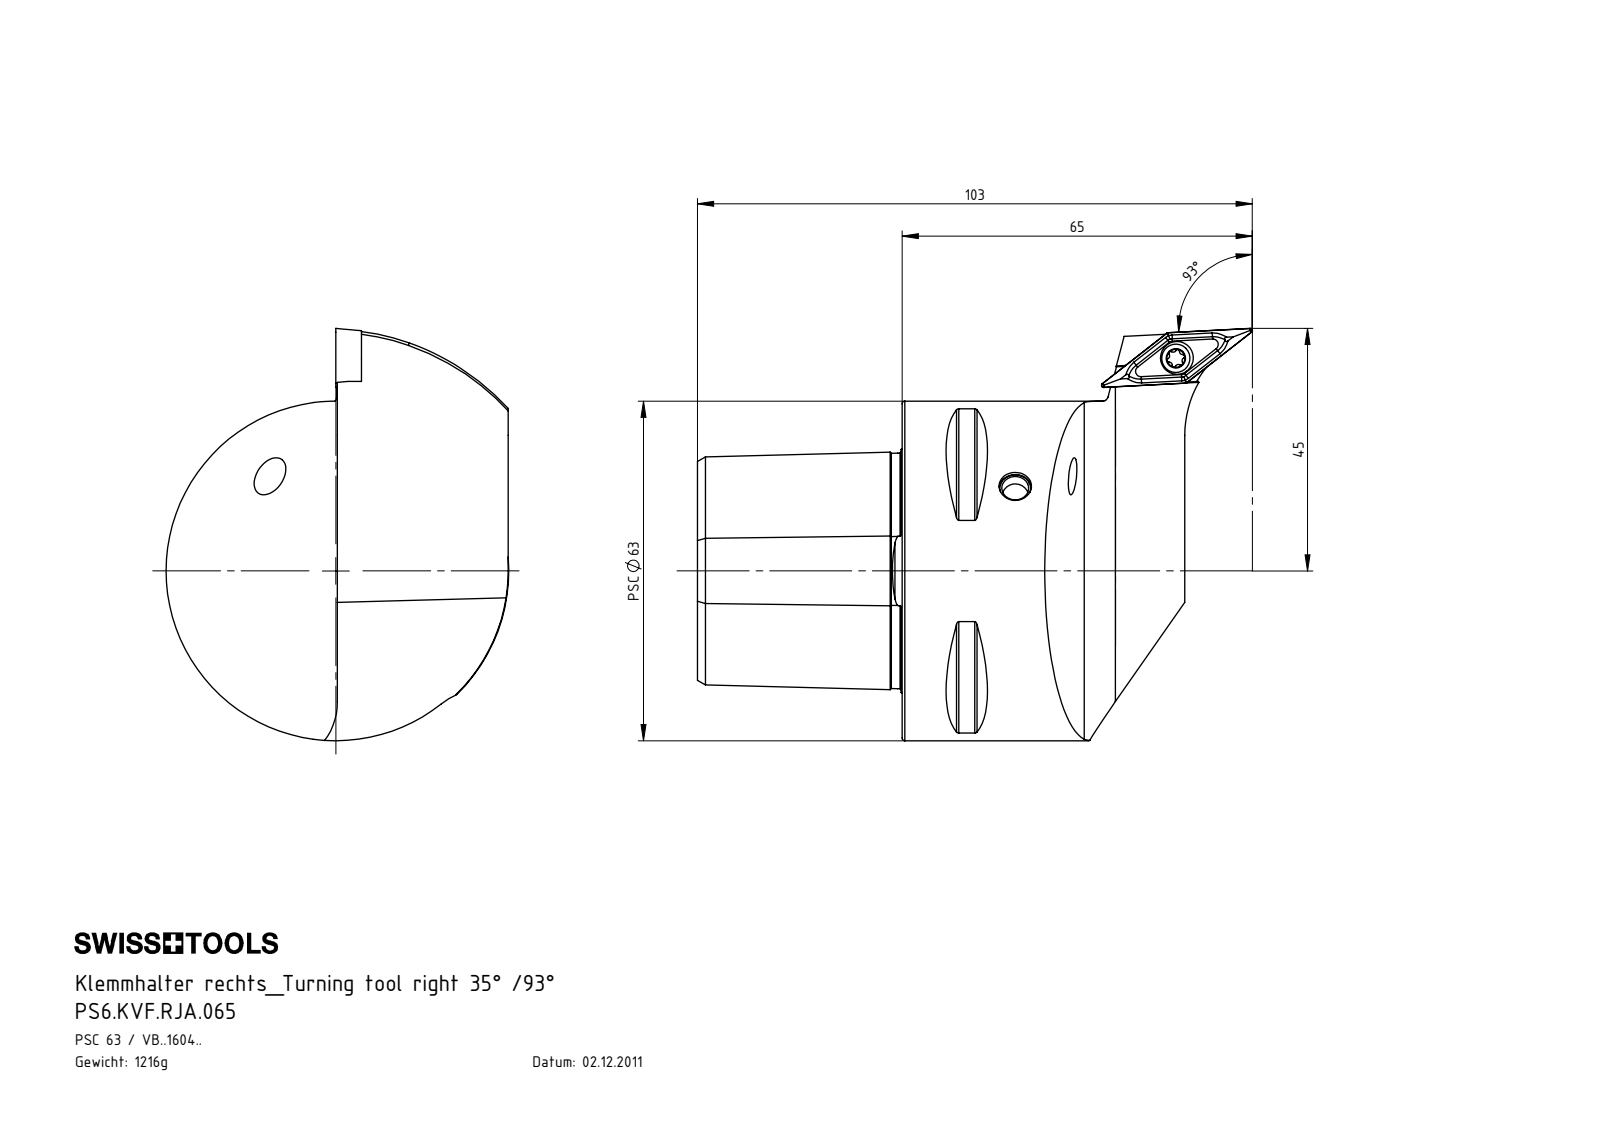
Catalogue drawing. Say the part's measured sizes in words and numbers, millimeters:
The part is named "KVT_MB_600_060; WCB-ER2.001.009_A; VBMT160404; PS6-KVF.RJA.065_A (+1 more)". Its 3-D file was written by "SolidWorks 2017 (AUTOMOTIVE_DESIGN)". It is 5 solids with 275 faces: 57 planar, 69 cylindrical and 149 other. Overall it measures 103 by 76.5 by 63.61 millimeters. Its volume is 152 700 cubic millimeters and its surface area 27 674 square millimeters. Round holes: 2 of diameter 5, 1 of diameter 3.3, 1 of diameter 4, 1 of diameter 4.4, 1 of diameter 6.1, 1 of diameter 8.1, 1 of diameter 18, 1 of diameter 28, 1 of diameter 32. Round bosses or shafts: 1 of diameter 63, 1 of diameter 6, 1 of diameter 5.25, 1 of diameter 4. Partial cylindrical surfaces (rounded edges, fillets, slot ends): 8 of radius 0.5, 6 of radius 0.34, 6 of radius 0.59, 2 of radius 0.15, 2 of radius 6, 2 of radius 32, 1 of radius 11. The main face-to-face distances are 38, 24.88, 27, 11, 4.46, 55.8, 27.24, 31.7, 37.8, 10.8. The hole center spacings are 27.5, 55.33, 55.53, 77.15, 77.37.
